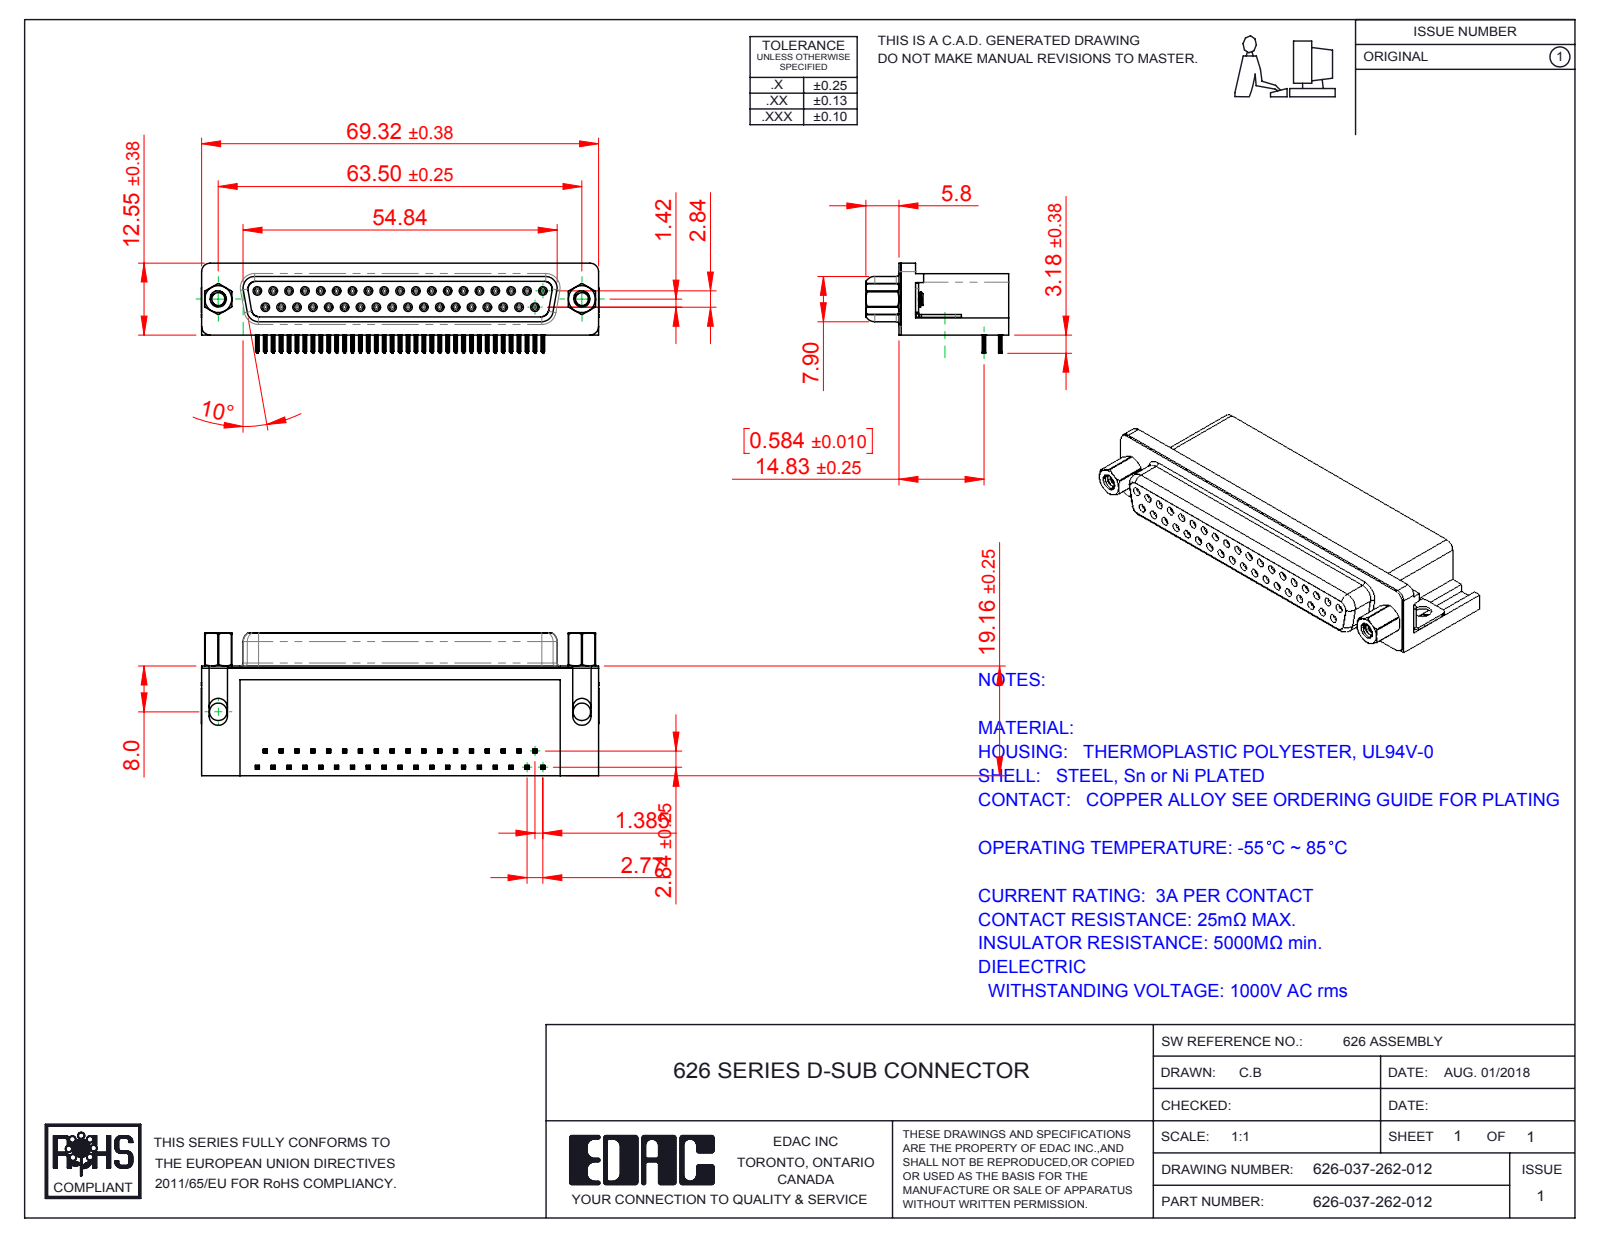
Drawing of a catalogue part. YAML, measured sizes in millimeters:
part_name: "626 Contact Top; 626 Housing_37 Socket; 626 Contact Bottom; 626 Thru Hole Board Mount (+3 more)"
step_written_by: "SolidWorks 2016 (CONFIG_CONTROL_DESIGN)"
units: millimeters
bodies: {solids: 43, faces: 5598, planar: 2508, cylindrical: 1332, other: 1758}
overall_size: [69.4, 24.96, 15.73]
volume: 14839
surface_area: 15486
round_holes:
  - {diameter: 0.8, count: 37}
  - {diameter: 0.9, count: 37}
  - {diameter: 2.29, count: 2}
  - {diameter: 3.05, count: 2}
  - {diameter: 4, count: 2}
  - {diameter: 4.8, count: 2}
  - {diameter: 5, count: 2}
round_bosses_or_shafts:
  - {diameter: 1.2, count: 37}
  - {diameter: 4.9, count: 2}
  - {diameter: 2.79, count: 2}
partial_cylinders:
  - {radius: 0.1, count: 296}
  - {radius: 0.15, count: 148}
  - {radius: 0.35, count: 74}
  - {radius: 0.34, count: 37}
  - {radius: 0.28, count: 18}
  - {radius: 1, count: 18}
  - {radius: 1.35, count: 8}
  - {radius: 1.6, count: 8}
face_to_face_distances: [0.4, 10.34, 2.84, 6.2, 18.76, 6.65, 0.85, 0.45, 7.1, 7.05]
hole_center_spacings: [3.16, 2.77, 5.54, 8.31, 11.08, 22.16, 13.85, 19.39]
